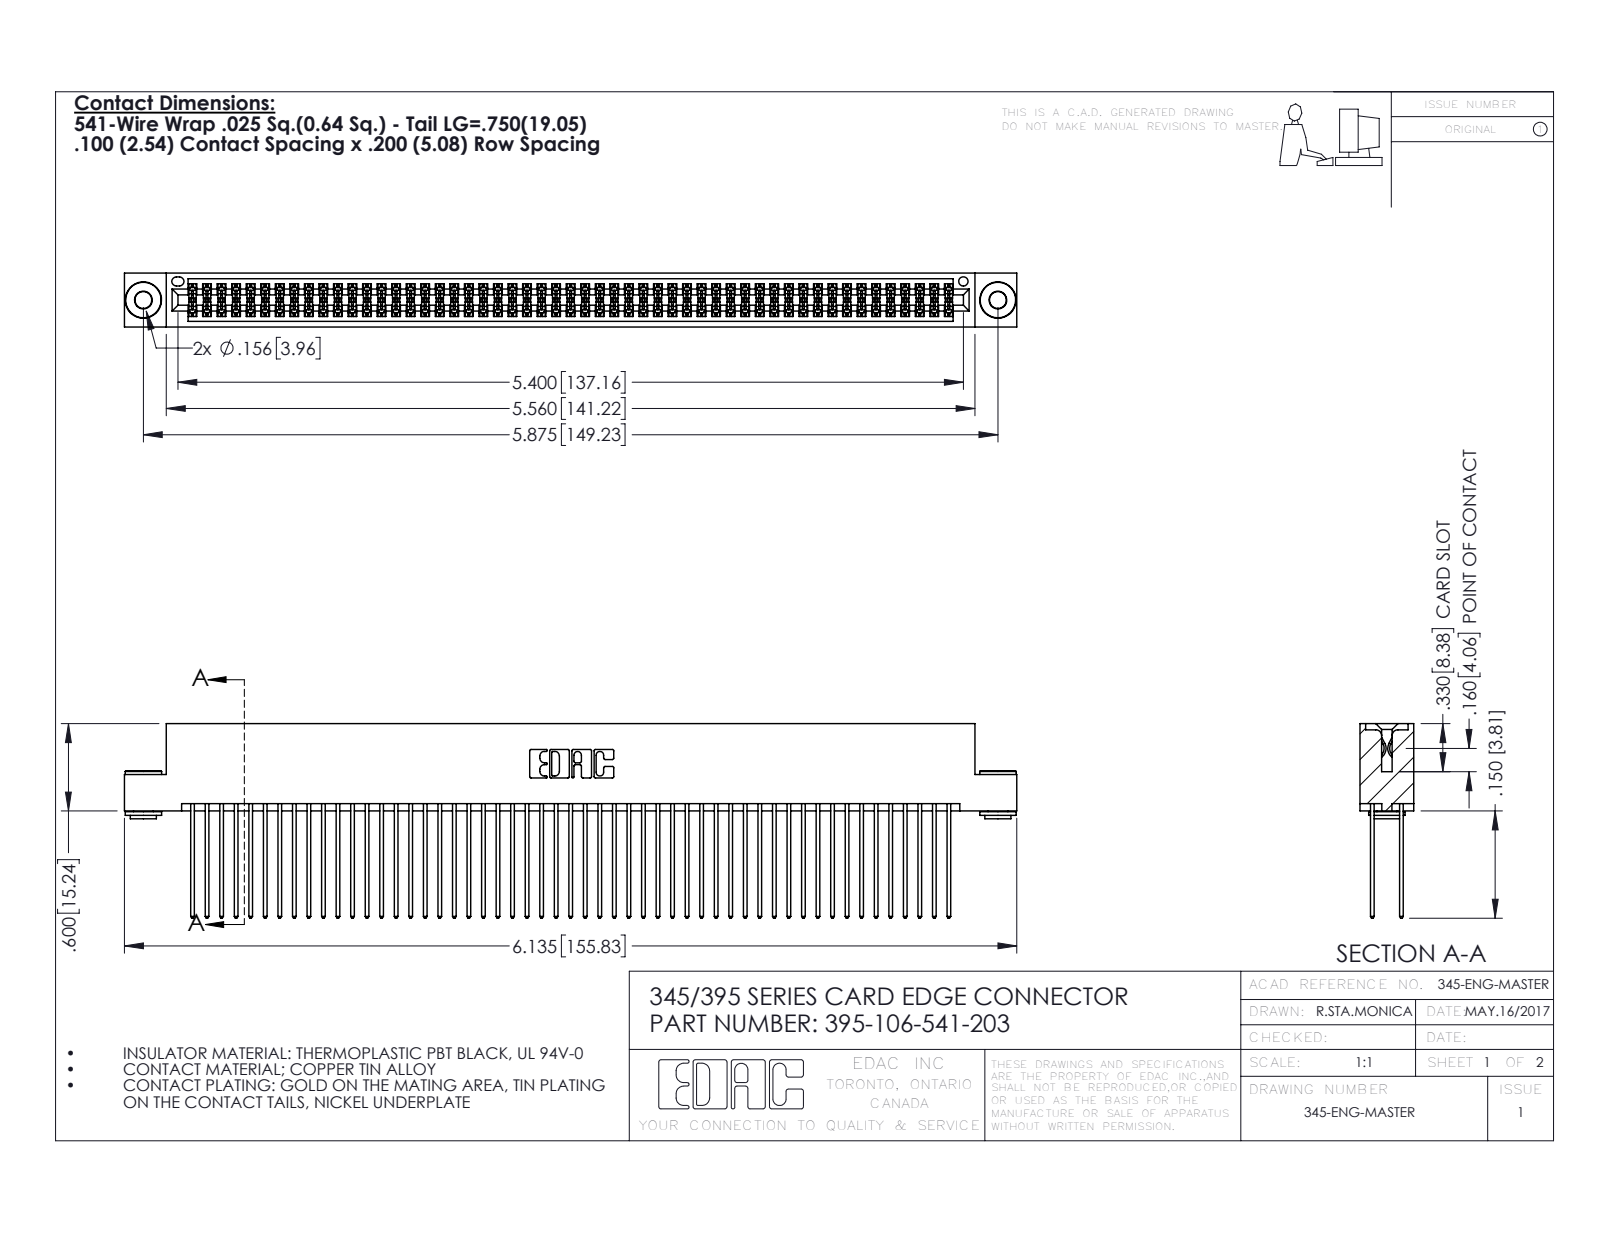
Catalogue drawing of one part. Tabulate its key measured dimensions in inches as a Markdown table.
| quantity | value |
| --- | --- |
| part name | 345-292-001_345-293-141; 345-250-002_345-250-002-102; 345 Part_Flush Mounting Lugs - 0.156 Dia-TH; 395-106-541-203 |
| STEP written by | SolidWorks 2016 (CONFIG_CONTROL_DESIGN) |
| units | inches |
| bodies | 109 solids, 5464 faces (3588 planar, 1868 cylindrical, 8 other) |
| overall size | 6.135 × 1.337 × 0.37 |
| volume | 0.968 in³ |
| surface area | 41.43 in² |
| round holes (diameter × count) | 0.116 × 2, 0.156 × 2, 0.064 × 1 |
| round bosses / shafts (diameter × count) | 0.25 × 2, 0.18 × 2, 0.136 × 2 |
| partial cylindrical surfaces (radius × count) | 0.006 × 159, 0.01 × 106, 0.01 × 22, 0.007 × 6, 0.031 × 6, 0.026 × 3, 0.014 × 2, 0.019 × 2 |
| main face-to-face distances | 0.072, 0.298, 0.2, 0.025, 0.098, 0.272, 0.225, 0.37, 0.175, 0.149 |
| hole center spacings | 0.27, 5.639, 5.875 |
